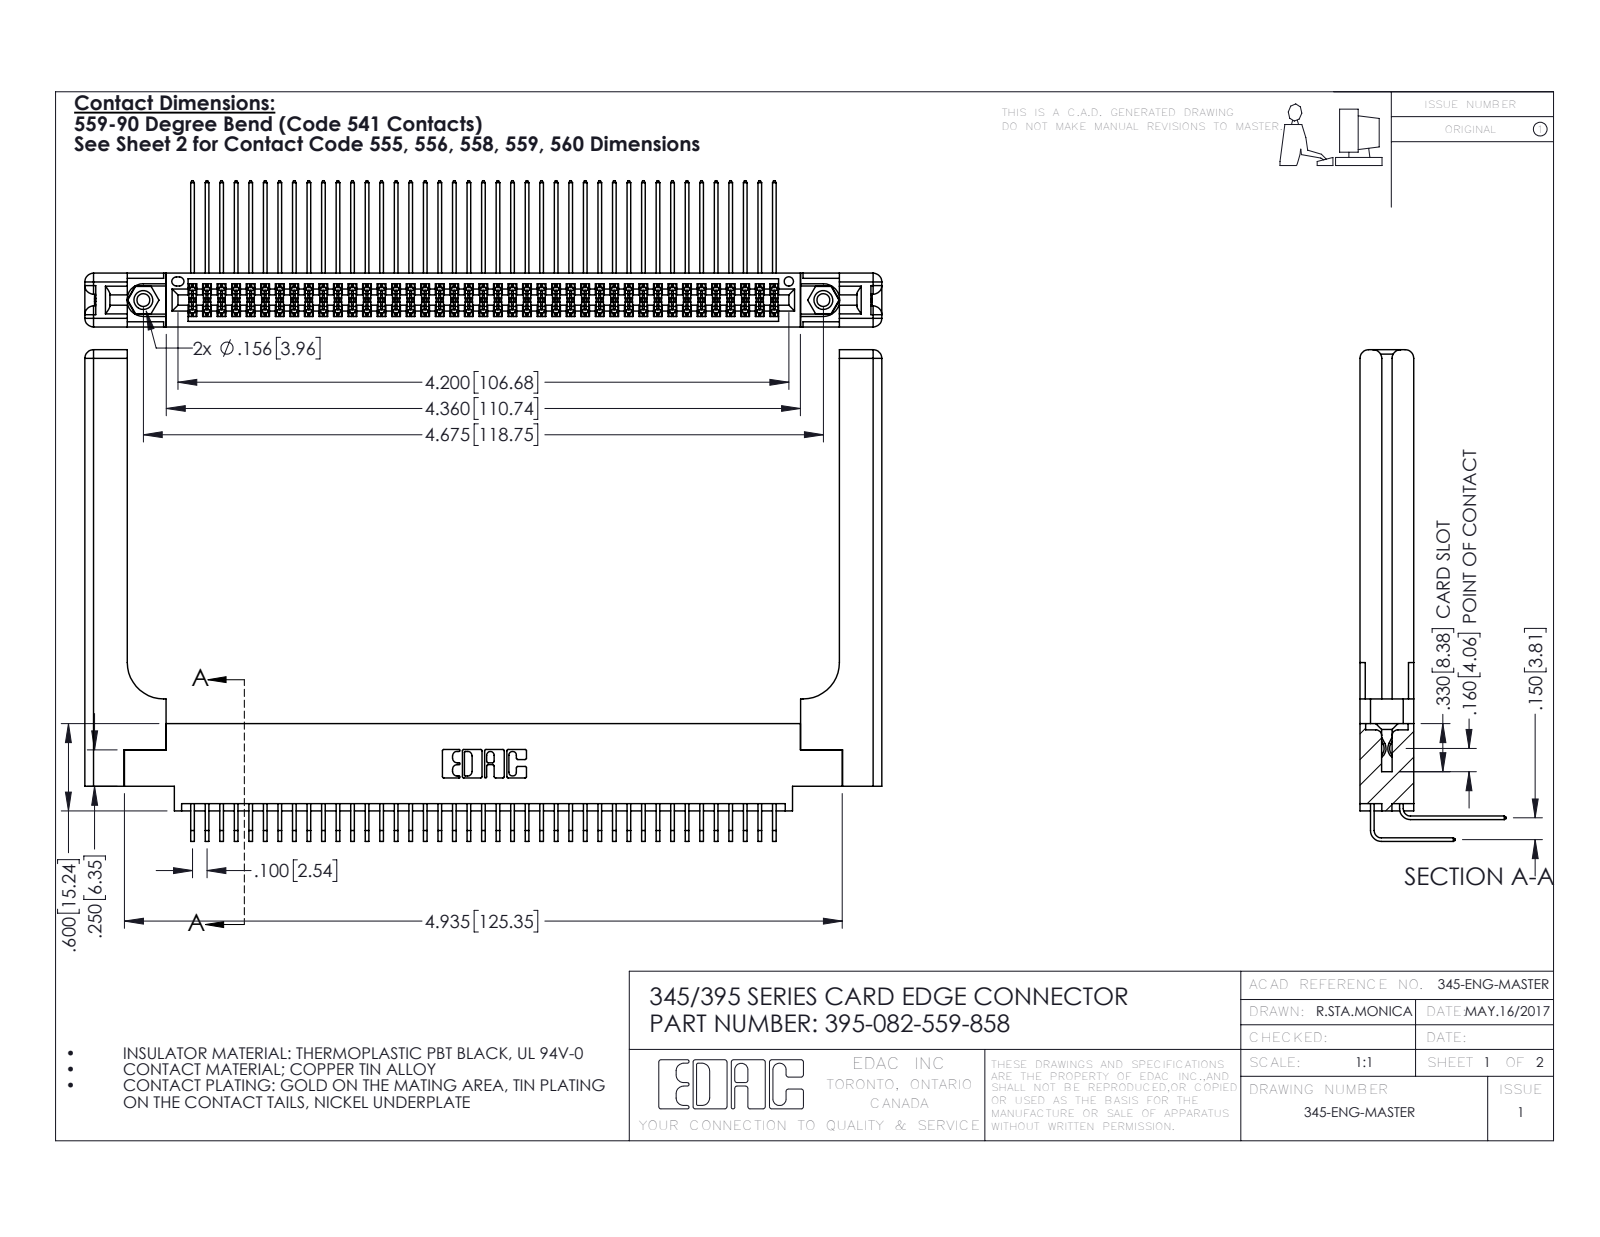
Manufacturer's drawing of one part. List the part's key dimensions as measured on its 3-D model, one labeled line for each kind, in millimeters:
Part name (STEP PRODUCT): 345 Part_0.170 Offset - 0.156 Dia-TH; 345-292-001_558 559 Tail - 1; 395-082-559-858; 345-250-001_345-250-001-102 (+2 more)
STEP written by: SolidWorks 2016 (CONFIG_CONTROL_DESIGN)
Units: millimetres
Bodies: 87 solids, 4650 faces (3102 planar, 1488 cylindrical, 60 other)
Overall size (bounding box): 139.2 × 85.8 × 25.5
Volume: 22 350 mm³ · Surface area: 27 910 mm²
Round holes (diameter × count): ⌀2.3 ×2, ⌀3.2 ×2, ⌀4 ×2, ⌀1.6 ×1
Round bosses / shafts (diameter × count): ⌀3.9 ×2
Partial cylindrical surfaces — rounded edges, fillets, slot ends (radius × count): R0.2 ×123, R0.3 ×22, R1.5 ×16, R0.2 ×6, R0.8 ×6, R0.7 ×3, R0.4 ×2, R0.5 ×2
Main face-to-face distances: 1.8, 9.4, 7.6, 2.5, 6.9, 0.6, 5.1, 5.7, 3.8, 4.4
Hole centre spacings: 6.9, 112.8, 118.7
